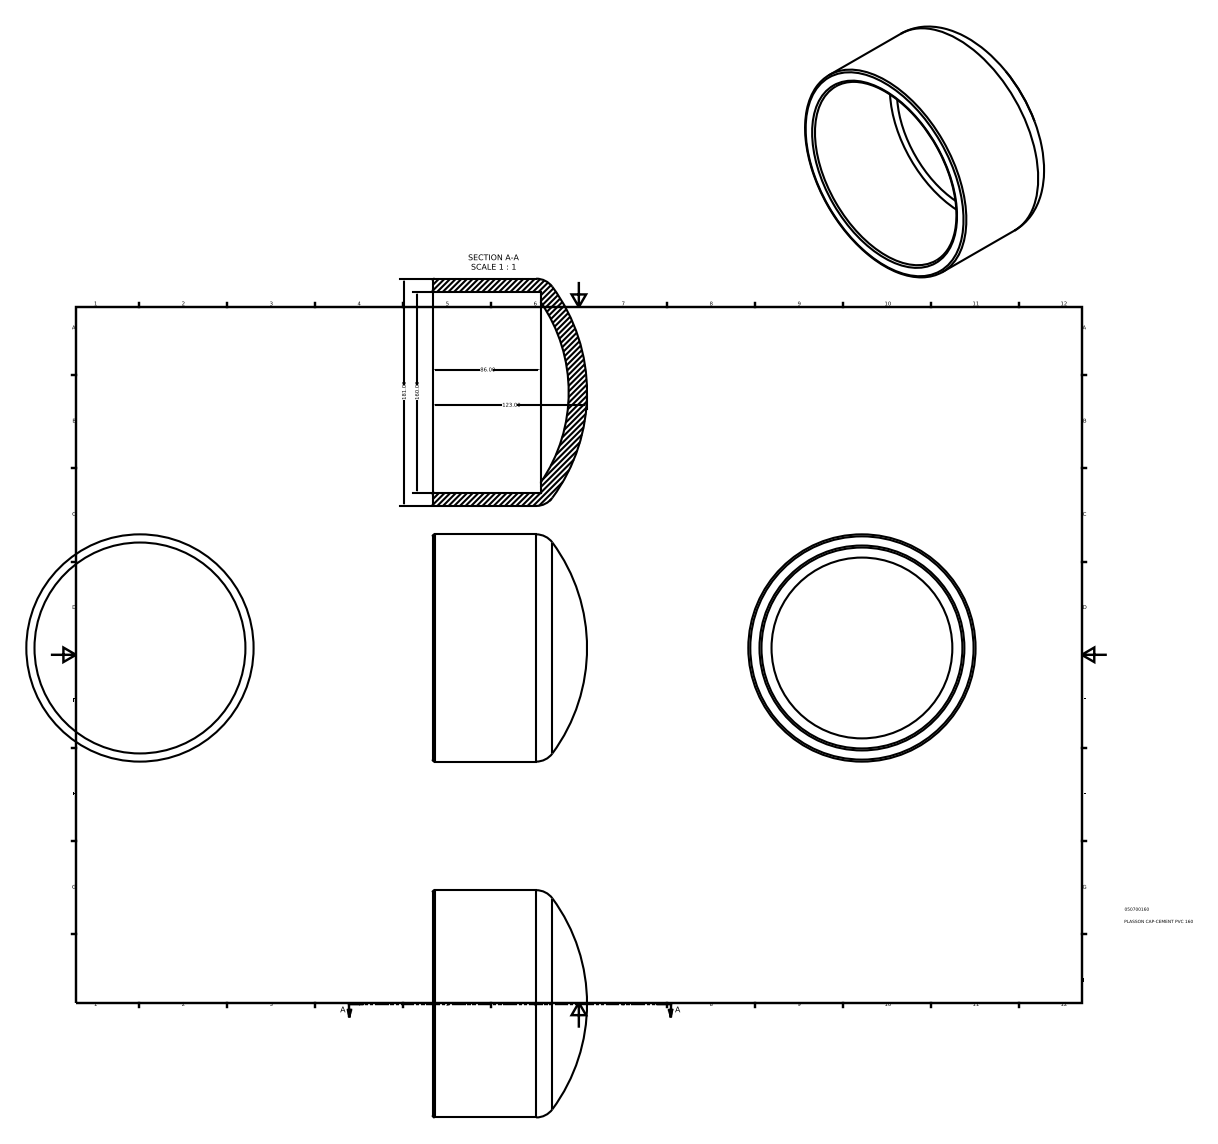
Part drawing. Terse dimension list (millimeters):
name: 050700160
written by: Autodesk Inventor 2015 (AUTOMOTIVE_DESIGN)
unit: mm
bodies: 1 solid, 9 faces (2 planar, 2 cylindrical, 5 other)
size: 181 × 181 × 123
volume: 839 534 mm³; area: 149 576 mm²
holes: 1× ⌀160
bosses: 1× ⌀181
face distances: 86
